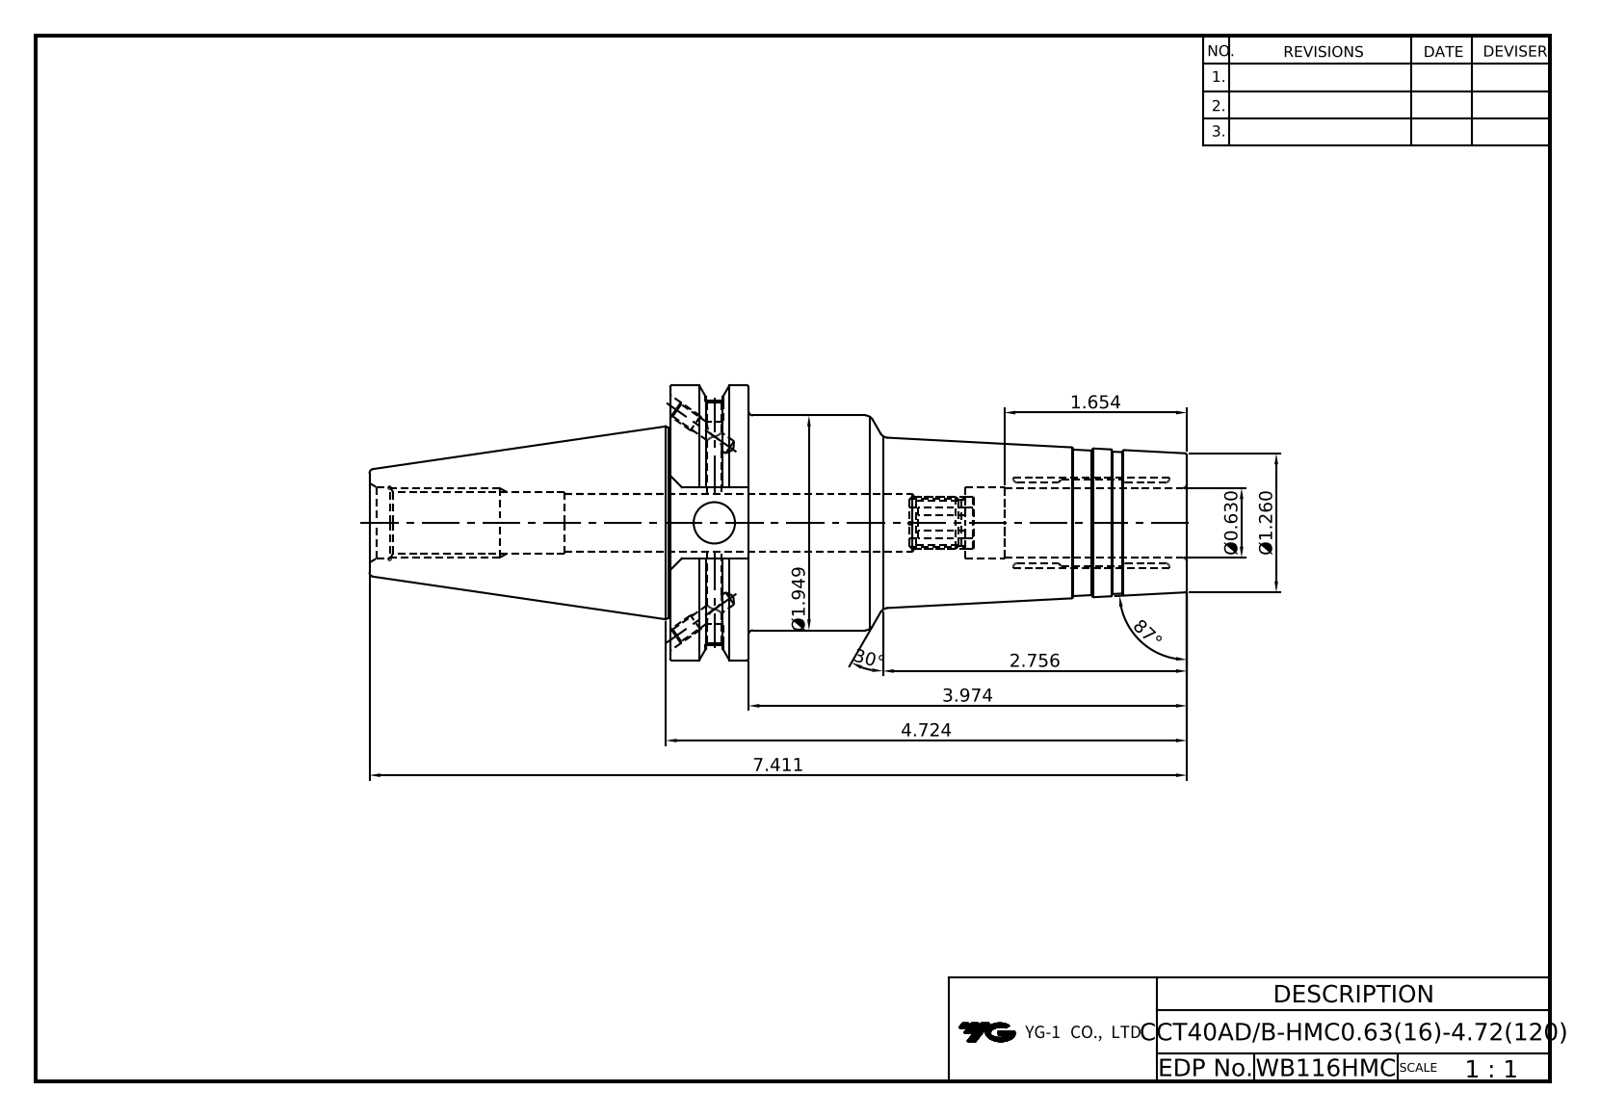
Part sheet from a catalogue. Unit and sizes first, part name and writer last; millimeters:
Units: millimetres
Overall size (bounding box): 188.25 × 63.5 × 61.09
Round holes (diameter × count): ⌀3.24 ×4, ⌀4 ×2, ⌀4.2 ×2, ⌀9.53 ×1, ⌀10.92 ×1, ⌀13 ×1, ⌀13.39 ×1, ⌀16 ×1, ⌀16.3 ×1, ⌀16.6 ×1
Round bosses / shafts (diameter × count): ⌀63.5 ×1, ⌀49.5 ×1, ⌀43.8 ×1
Partial cylindrical surfaces — rounded edges, fillets, slot ends (radius × count): R8.19 ×1, R28.15 ×1
Main face-to-face distances: 18.05, 119, 100.95, 47.6, 16.38, 69.25, 87.3, 188.25, 137.25, 68
Volume: 215 428 mm³ · Surface area: 37 444 mm²
Bodies: 1 solid, 106 faces (35 planar, 30 cylindrical, 41 other)
Part name (STEP PRODUCT): LO-CCT40ADB-HMC16-120
STEP written by: Autodesk Inventor 2022 (AUTOMOTIVE_DESIGN)
